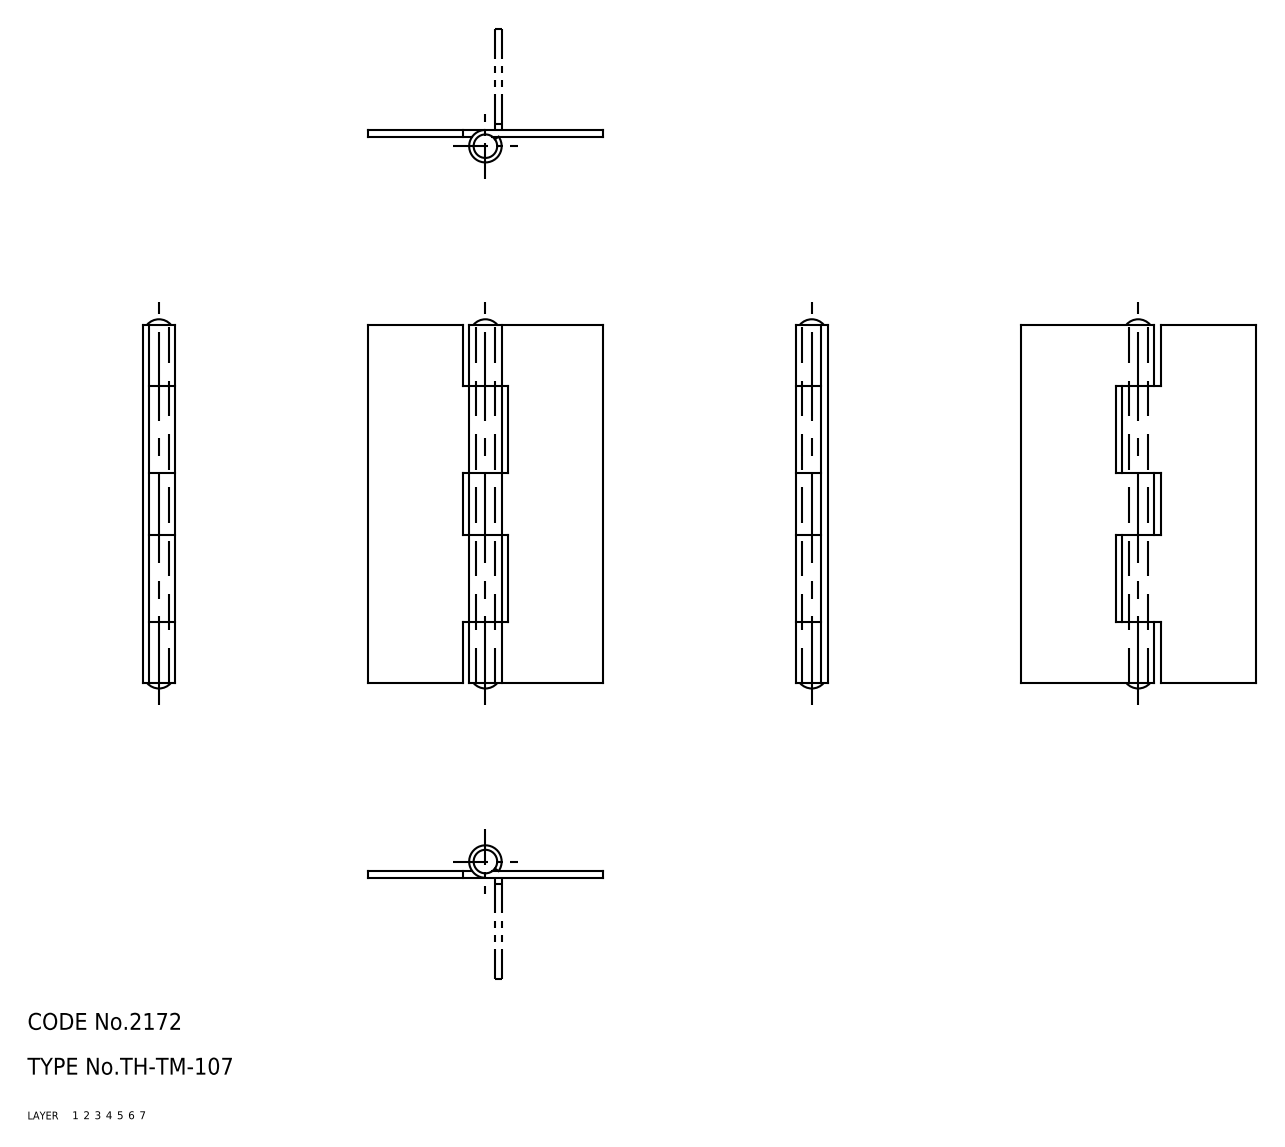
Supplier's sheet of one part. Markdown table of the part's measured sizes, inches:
| quantity | value |
| --- | --- |
| part name | 67110983; 67110996; 67111009 |
| STEP written by | CADfix (AUTOMOTIVE_DESIGN) |
| units | inches |
| bodies | 3 solids, 44 faces (0 planar, 0 cylindrical, 44 other) |
| overall size | 2.594 × 1.654 × 0.228 |
| volume | 0.272 in³ |
| surface area | 12 in² |
